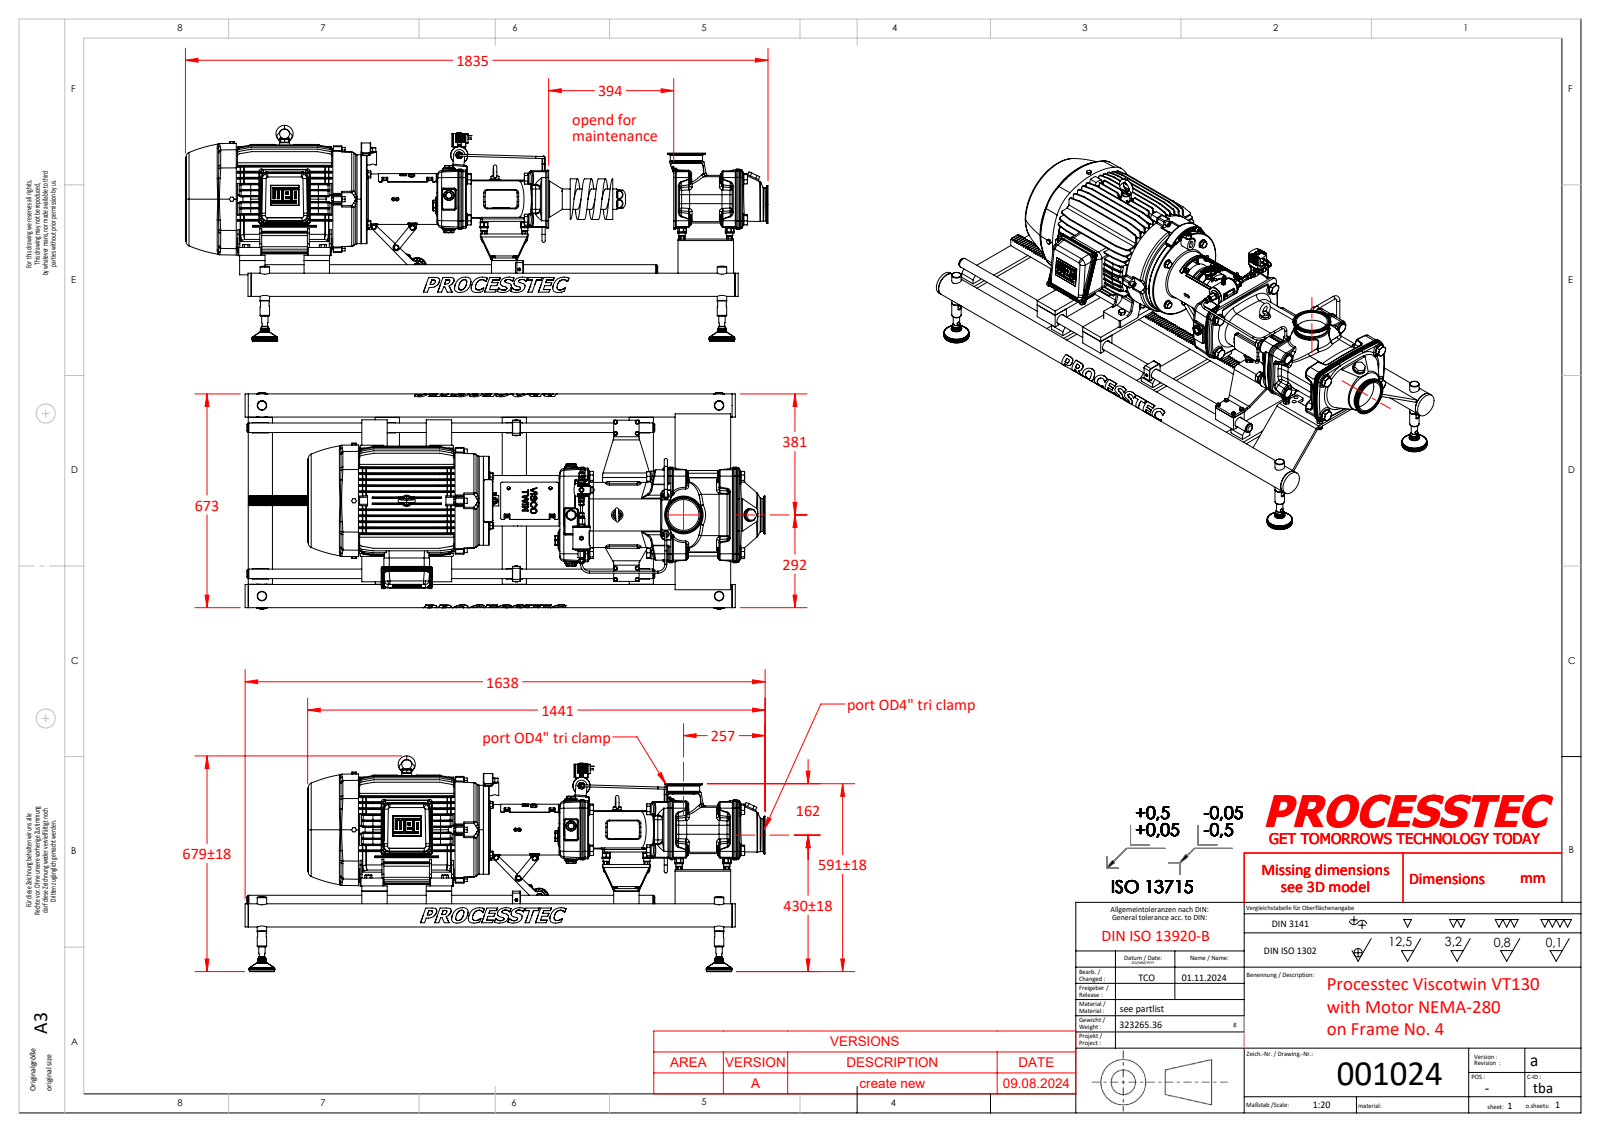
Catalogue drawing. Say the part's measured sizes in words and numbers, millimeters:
The part is named "000933_Standard; 001024 VT130 NEMA280 Frame-4; 001379_Standard; 001432_Standard (+8 more)". Its 3-D file was written by "SolidWorks 2023 (AUTOMOTIVE_DESIGN)". It is 228 solids with 15185 faces: 5033 planar, 3424 cylindrical and 6728 other. Overall it measures 1638 by 680.5 by 678.96 millimeters. Its volume is 82 730 000 cubic millimeters and its surface area 7 570 000 square millimeters. Round holes: 25 of diameter 8.5, 20 of diameter 5, 18 of diameter 6.8, 17 of diameter 10.2, 14 of diameter 10.5, 13 of diameter 13, 13 of diameter 17.5, 11 of diameter 4.1, 10 of diameter 11, 8 of diameter 6.4, 8 of diameter 10.1, 8 of diameter 10.25. Round bosses or shafts: 36 of diameter 10, 29 of diameter 6, 16 of diameter 20, 16 of diameter 8, 13 of diameter 24, 13 of diameter 12, 11 of diameter 17, 11 of diameter 4. Partial cylindrical surfaces (rounded edges, fillets, slot ends): 120 of radius 2, 95 of radius 3, 83 of radius 4, 77 of radius 1.5, 59 of radius 0.5, 50 of radius 6, 47 of radius 8, 30 of radius 9. The main face-to-face distances are 12.7, 8, 82.7, 70, 481, 99.1, 86.4, 16.4, 305, 786. The hole center spacings are 461.41, 400, 129.3, 230, 832.41, 55, 609.59, 800.
